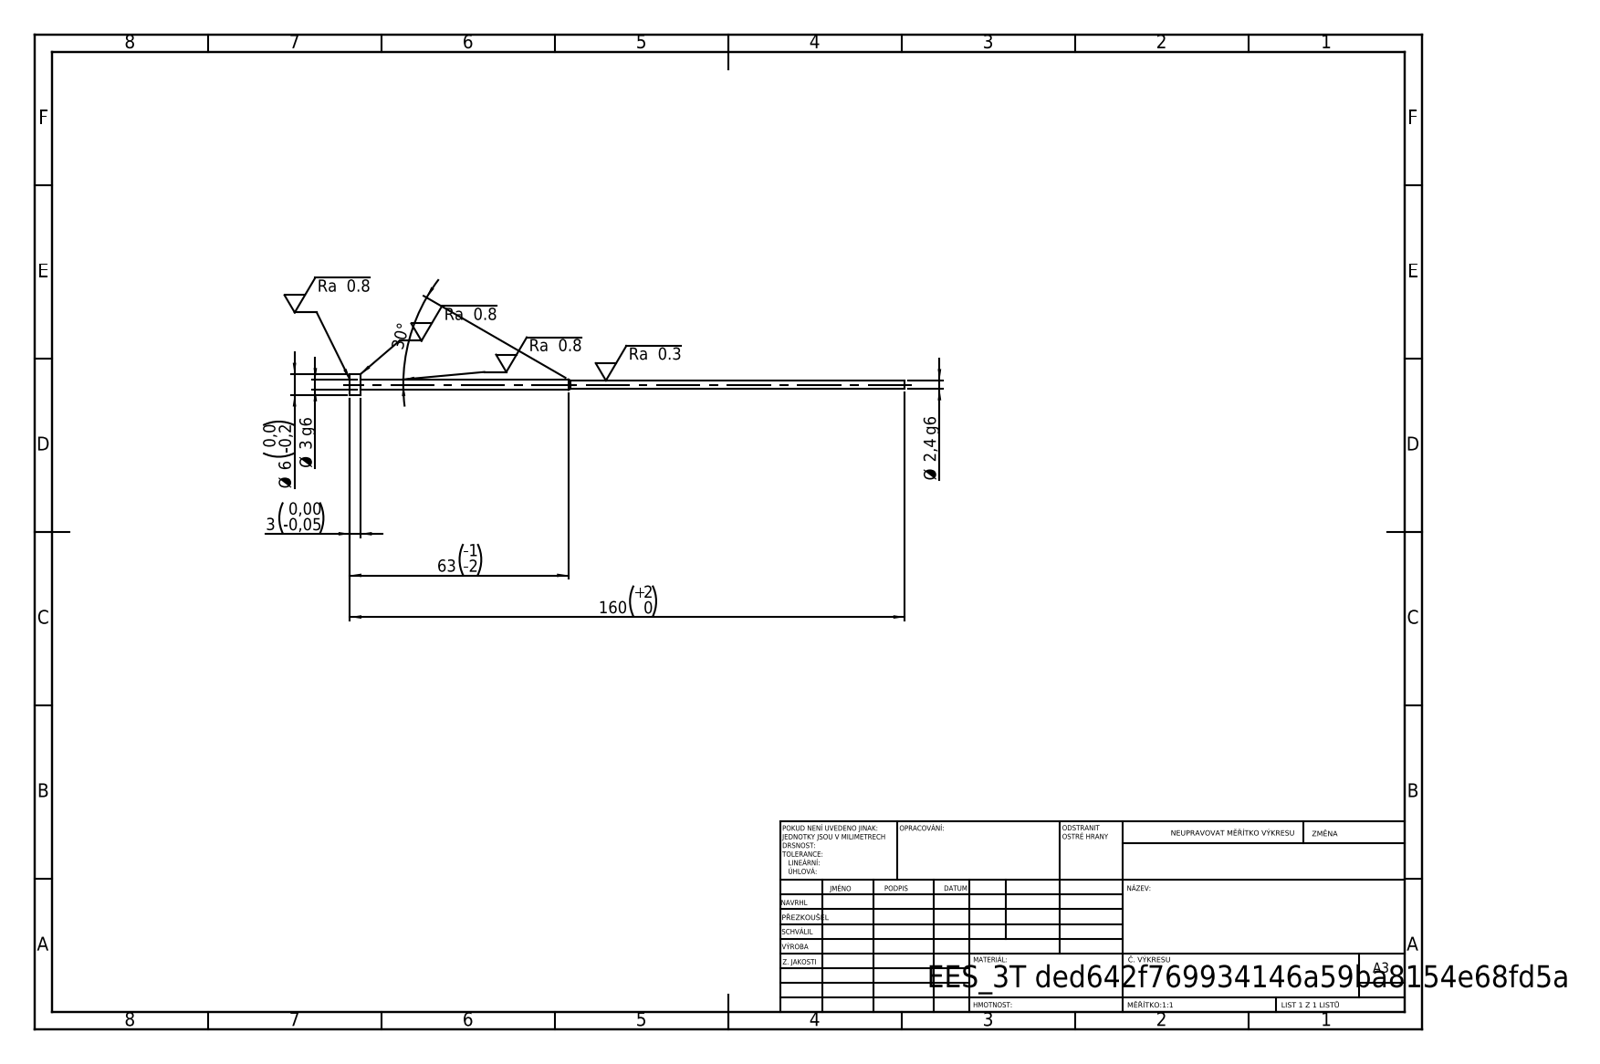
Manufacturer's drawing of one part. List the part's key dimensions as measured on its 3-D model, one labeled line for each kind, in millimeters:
STEP written by: SolidWorks 2019 (CONFIG_CONTROL_DESIGN)
Units: millimetres
Bodies: 1 solid, 11 faces (3 planar, 6 cylindrical, 2 other)
Overall size (bounding box): 160 × 6 × 6
Volume: 948 mm³ · Surface area: 1 409 mm²
Round bosses / shafts (diameter × count): ⌀6 ×1, ⌀3 ×1, ⌀2.4 ×1
Main face-to-face distances: 3, 157, 160
